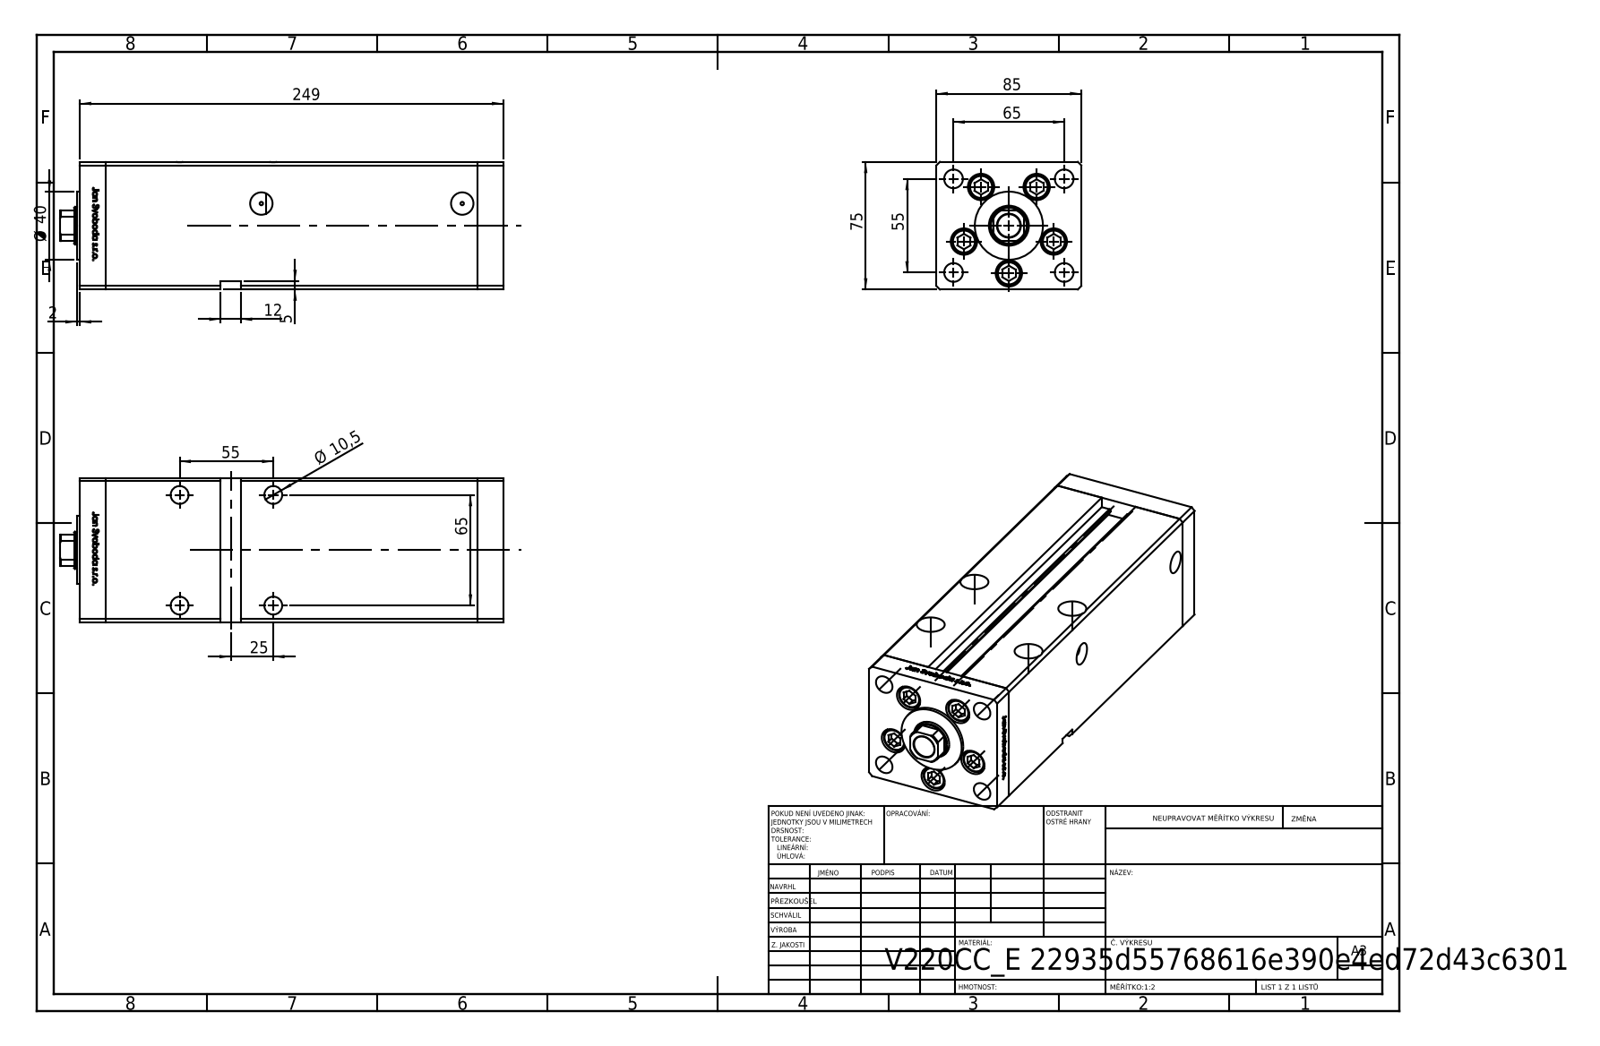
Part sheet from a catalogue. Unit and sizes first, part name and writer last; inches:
Units: inches
Overall size (bounding box): 10.236 × 3.346 × 2.953
Round holes (diameter × count): ⌀0.433 ×9, ⌀0.61 ×5, ⌀0.413 ×4, ⌀0.65 ×4, ⌀0.079 ×2, ⌀0.518 ×2, ⌀0.531 ×1, ⌀0.866 ×1, ⌀0.925 ×1
Round bosses / shafts (diameter × count): ⌀0.571 ×5, ⌀0.315 ×5, ⌀1.575 ×1
Partial cylindrical surfaces — rounded edges, fillets, slot ends (radius × count): R0.037 ×2, R0.413 ×1
Main face-to-face distances: 3.346, 2.953, 0.591, 8.602, 9.193, 9.783, 0.413, 2.539, 1.348, 2.697
Hole centre spacings: 1.102, 1.676, 2.165, 2.559, 3.352, 0.664, 0.755, 1.273
Volume: 81.83 in³ · Surface area: 324.3 in²
Bodies: 14 solids, 1214 faces (475 planar, 165 cylindrical, 574 other)
Part name (STEP PRODUCT): V220C_FRONT_E; V220C_E MIDDLE; V220C_VC_E; V220C BACK_E (+1 more)
STEP written by: SolidWorks 2019 (CONFIG_CONTROL_DESIGN)
